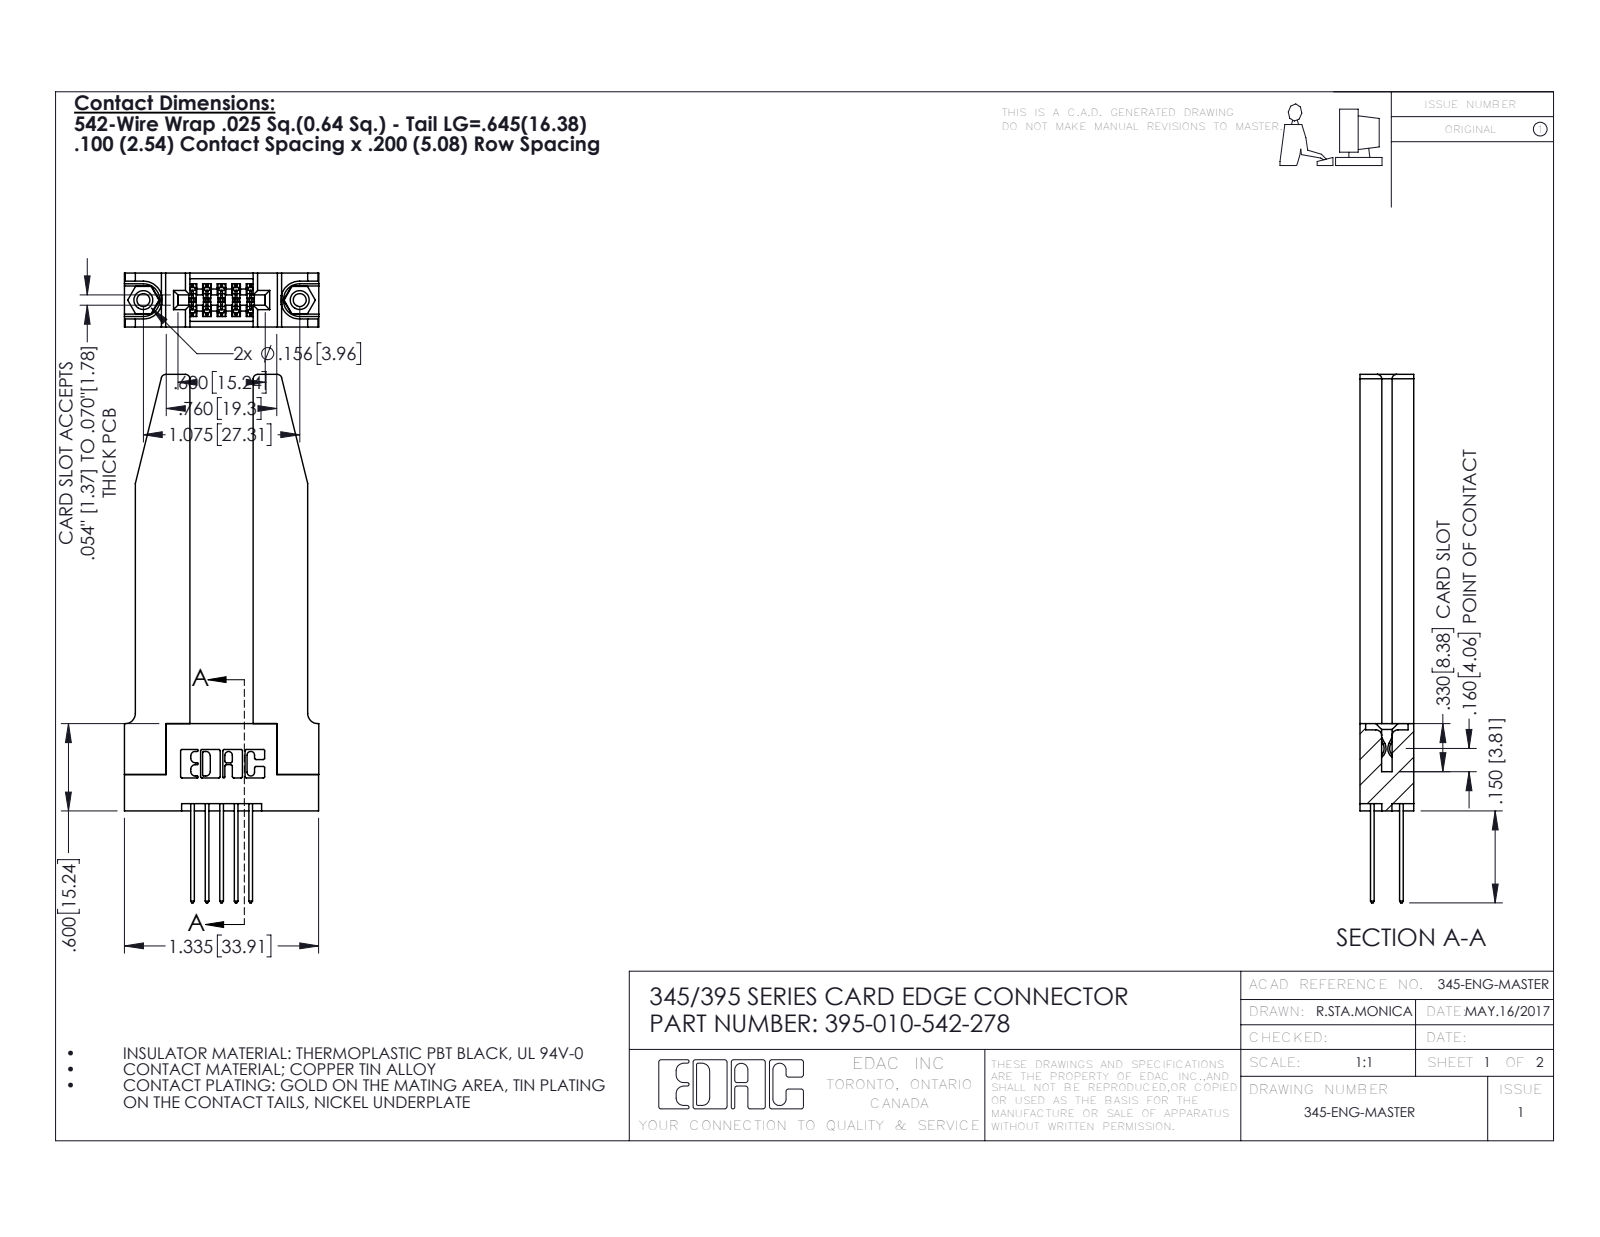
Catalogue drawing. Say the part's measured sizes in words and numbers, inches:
The part is named "345-250-001_345-250-001-102; 345 Part_Flush Mounting Lugs - 0.156 Dia-TH; 395-010-542-278; 345-220-078_345-220-078 (+1 more)". Its 3-D file was written by "SolidWorks 2016 (CONFIG_CONTROL_DESIGN)". It is 15 solids with 860 faces: 552 planar, 256 cylindrical and 52 other. Overall it measures 3.632 by 1.336 by 0.37 inches. Its volume is 0.657 cubic inches and its surface area 16.7 square inches. Round holes: 2 of diameter 0.089, 2 of diameter 0.125, 2 of diameter 0.156, 1 of diameter 0.064. Round bosses or shafts: 2 of diameter 0.155. Partial cylindrical surfaces (rounded edges, fillets, slot ends): 22 of radius 0.01, 15 of radius 0.006, 10 of radius 0.01, 8 of radius 0.03, 6 of radius 0.007, 6 of radius 0.031, 3 of radius 0.026, 2 of radius 0.014. The main face-to-face distances are 0.37, 0.15, 0.22, 0.072, 0.148, 0.077, 0.298, 0.2, 0.435, 0.095. The hole center spacings are 0.27, 0.847, 1.075.
